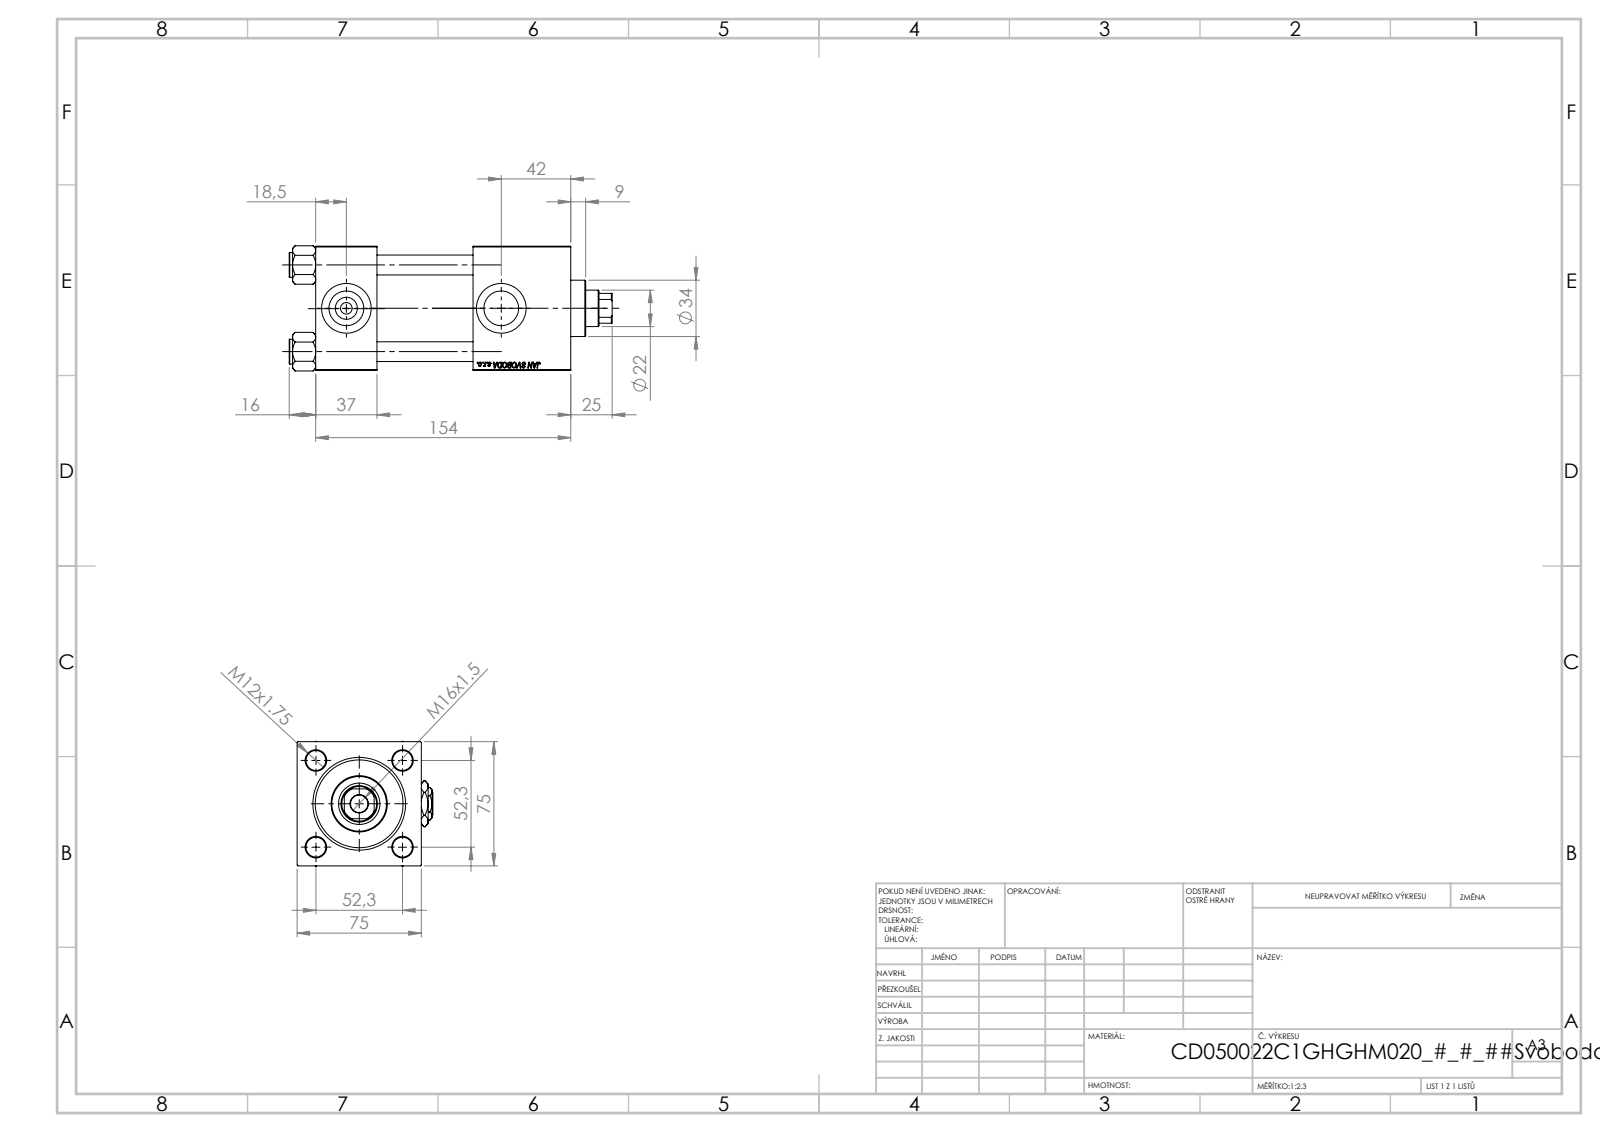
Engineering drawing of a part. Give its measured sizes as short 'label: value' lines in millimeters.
name: V215CD_C_TYCINKA; Zatka_pro_OIL_PORT; V215CD_VC_C; NUT_M5_V215CD_C (+2 more)
written by: SolidWorks 2019 (CONFIG_CONTROL_DESIGN)
unit: mm
bodies: 12 solids, 1195 faces (549 planar, 90 cylindrical, 556 other)
size: 195 × 82 × 75.54
volume: 653 522 mm³; area: 149 265 mm²
holes: 4× ⌀12, 2× ⌀7, 2× ⌀20.96, 2× ⌀30, 1× ⌀10.5, 1× ⌀22, 1× ⌀25, 1× ⌀41, 1× ⌀50, 1× ⌀53
bosses: 4× ⌀15, 1× ⌀56, 1× ⌀34
rounds: 1× R10.5
face distances: 75, 37, 154, 117, 95, 59, 58, 125.3, 88.3, 30.3
hole spacings: 36.98, 52.3, 73.96, 93.5
